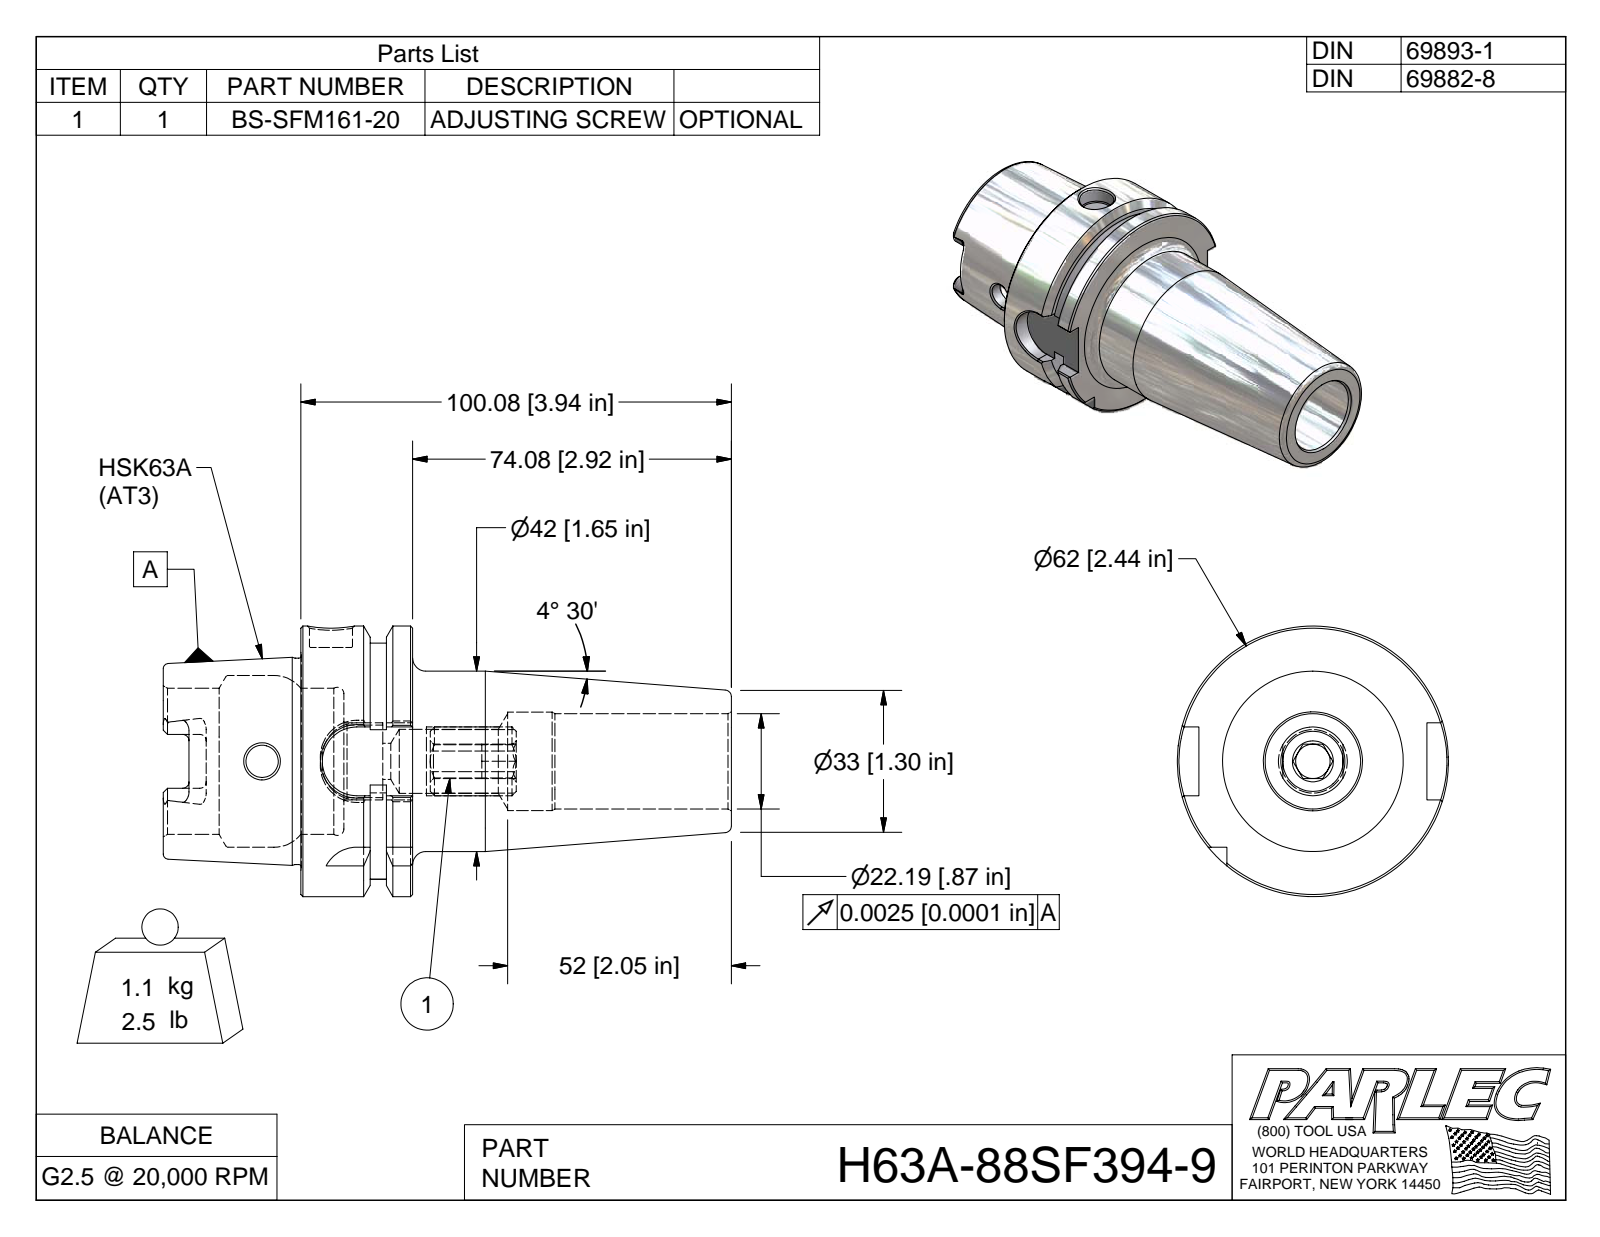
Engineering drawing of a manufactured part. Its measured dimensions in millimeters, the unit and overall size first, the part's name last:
Units: millimetres
Overall size (bounding box): 132.1 × 63 × 63
Round holes (diameter × count): ⌀7.5 ×1, ⌀10 ×1, ⌀16.9 ×1, ⌀22.2 ×1, ⌀23 ×1, ⌀34 ×1, ⌀40 ×1
Round bosses / shafts (diameter × count): ⌀63 ×1, ⌀48 ×1, ⌀42 ×1
Partial cylindrical surfaces — rounded edges, fillets, slot ends (radius × count): R1.5 ×6, R8 ×5, R2.9 ×4, R27.5 ×1
Main face-to-face distances: 26, 6.1, 9.9, 10, 16, 32, 58, 42, 74.1, 48.1
Volume: 146 500 mm³ · Surface area: 36 920 mm²
Bodies: 2 solids, 157 faces (58 planar, 35 cylindrical, 64 other)
Part name (STEP PRODUCT): H63A-88SF394-9; H63A-88SF394-9-1; BS-SFM161-20
STEP written by: Autodesk Inventor 2009 (AUTOMOTIVE_DESIGN)
